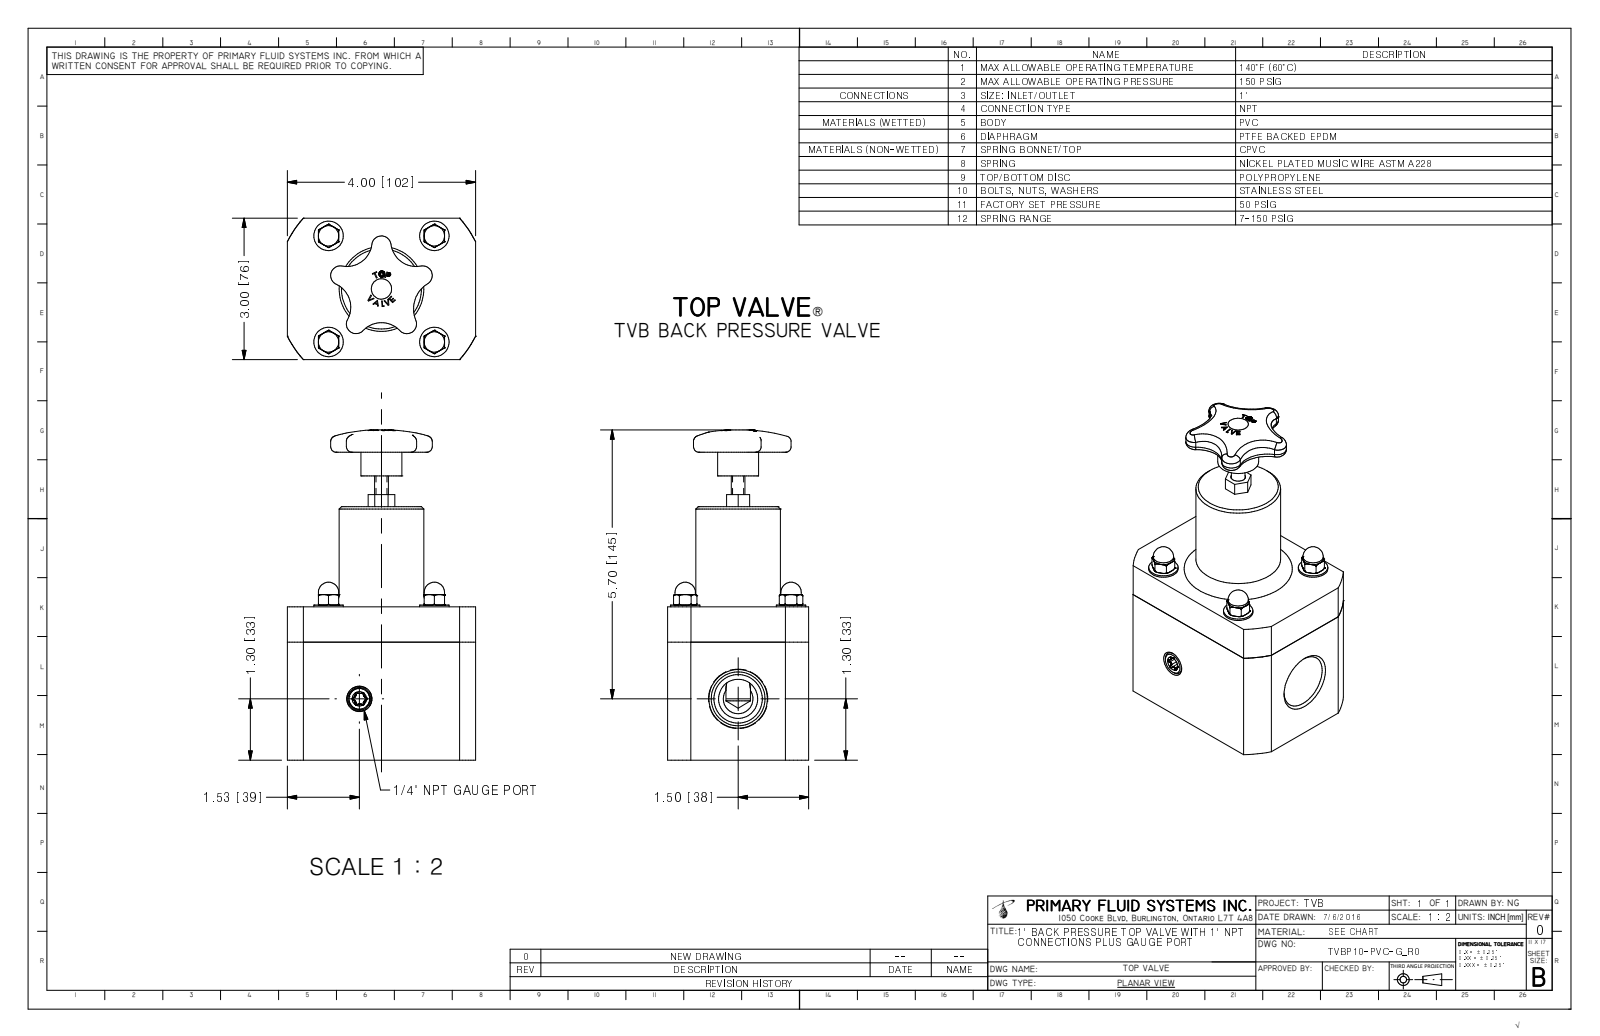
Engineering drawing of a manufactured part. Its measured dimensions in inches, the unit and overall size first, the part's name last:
Units: inches
Overall size (bounding box): 7.002 × 4 × 3
Round holes (diameter × count): ⌀0.175 ×4, ⌀1.144 ×1
Round bosses / shafts (diameter × count): ⌀0.625 ×4, ⌀0.433 ×4, ⌀0.375 ×4, ⌀1.8 ×1, ⌀0.87 ×1, ⌀0.293 ×1
Partial cylindrical surfaces — rounded edges, fillets, slot ends (radius × count): R0.027 ×6, R0.085 ×5, R0.205 ×5, R0.536 ×4, R0.656 ×4, R0.625 ×1, R0.745 ×1, R2.238 ×1
Main face-to-face distances: 3, 3.25, 4, 5.375, 2.125, 1, 2, 3.286, 0.036, 2.089
Hole centre spacings: 2.25, 3.182
Volume: 42.87 in³ · Surface area: 100.6 in²
Bodies: 1 solid, 367 faces (156 planar, 55 cylindrical, 156 other)
Part name (STEP PRODUCT): TVBP10-PVC-G_R0
STEP written by: Autodesk Inventor 2009 (AUTOMOTIVE_DESIGN)
